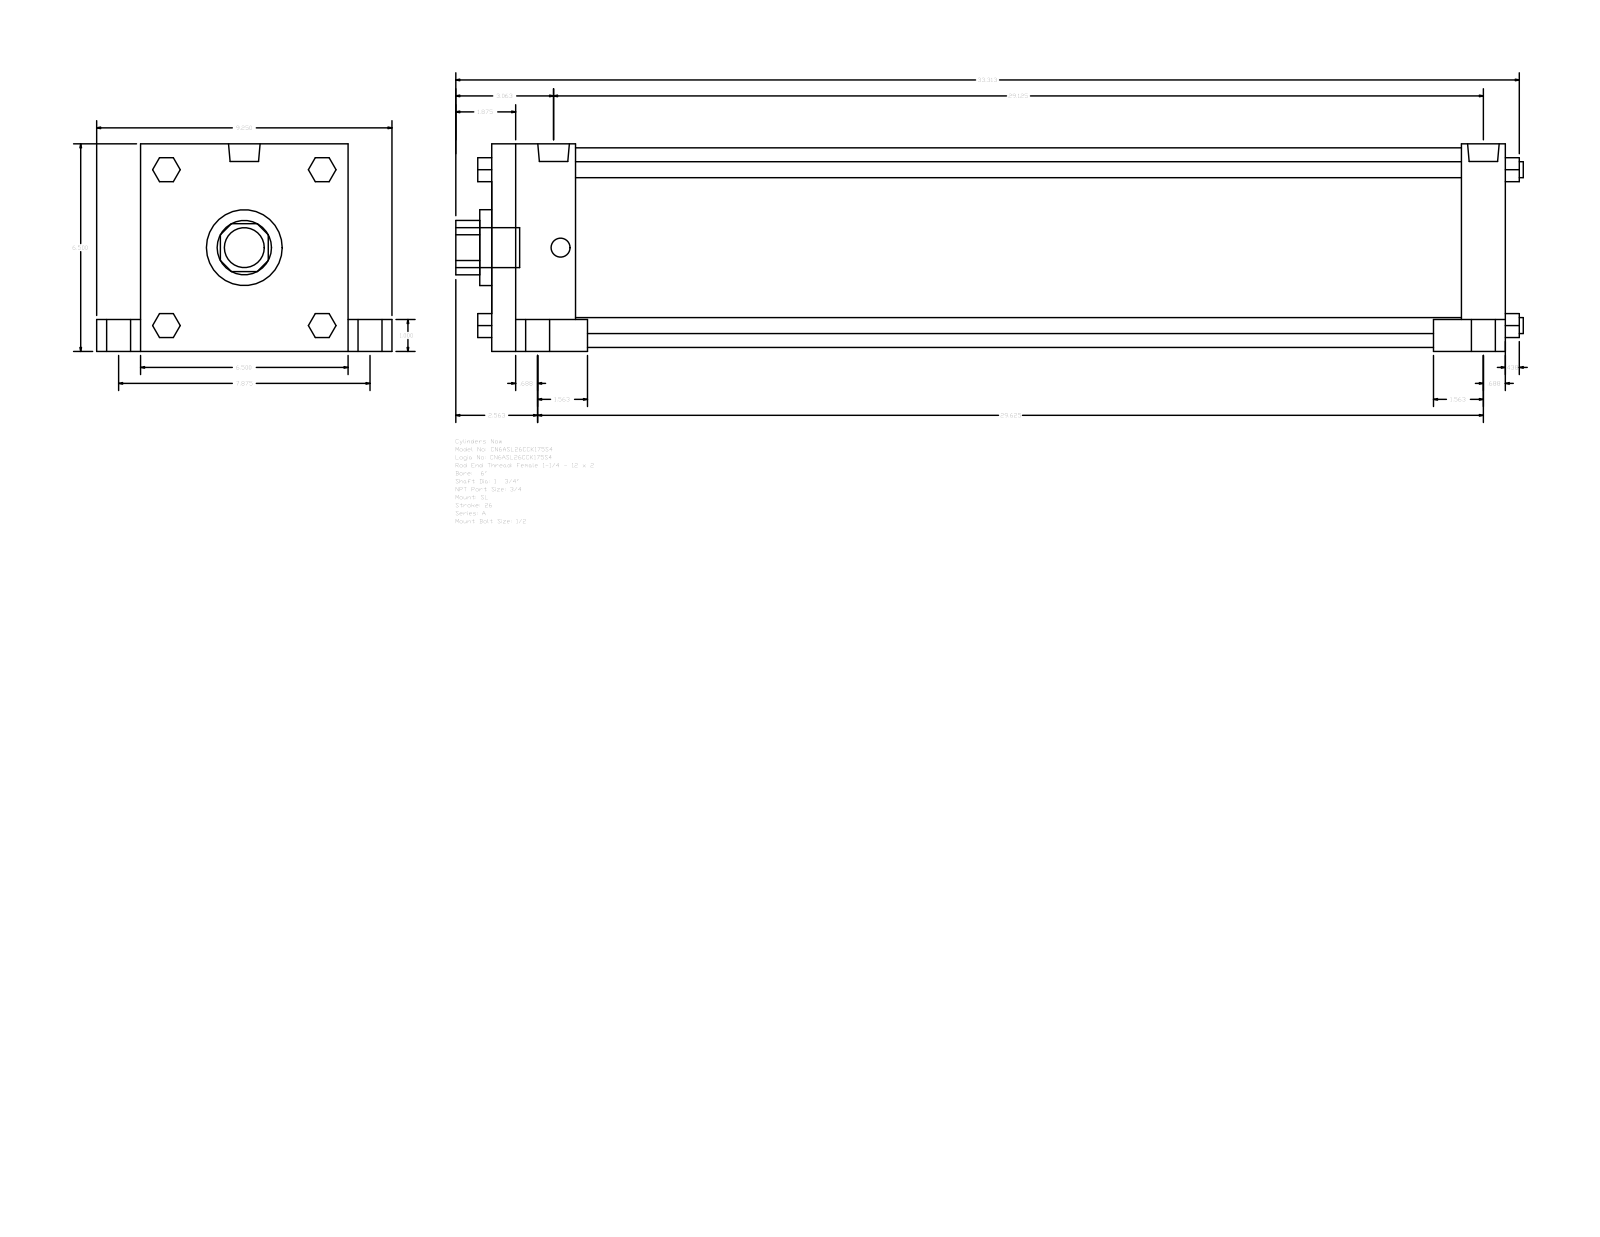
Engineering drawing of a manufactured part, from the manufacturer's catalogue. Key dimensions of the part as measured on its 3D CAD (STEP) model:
Part name (STEP PRODUCT): A_SL__0600_1.75
STEP written by: GSSL Pune (CONFIG_CONTROL_DESIGN)
Units: millimetres
Bodies: 0 solids, 150 faces (114 planar, 36 cylindrical, 0 other)
Overall size (bounding box): 849.31 × 234.95 × 165.1
Round holes (diameter × count): ⌀44.45 ×1, ⌀60.33 ×1, ⌀158.75 ×1
Round bosses / shafts (diameter × count): ⌀25.4 ×4, ⌀19.05 ×4, ⌀15.08 ×4, ⌀12.7 ×4, ⌀25.12 ×2, ⌀31.75 ×1
Partial cylindrical surfaces — rounded edges, fillets, slot ends (radius × count): R21.63 ×1
Main face-to-face distances: 165.1, 806.45, 34.92, 66.68, 739.77, 771.53, 704.85, 25.4, 139.7, 200.02
